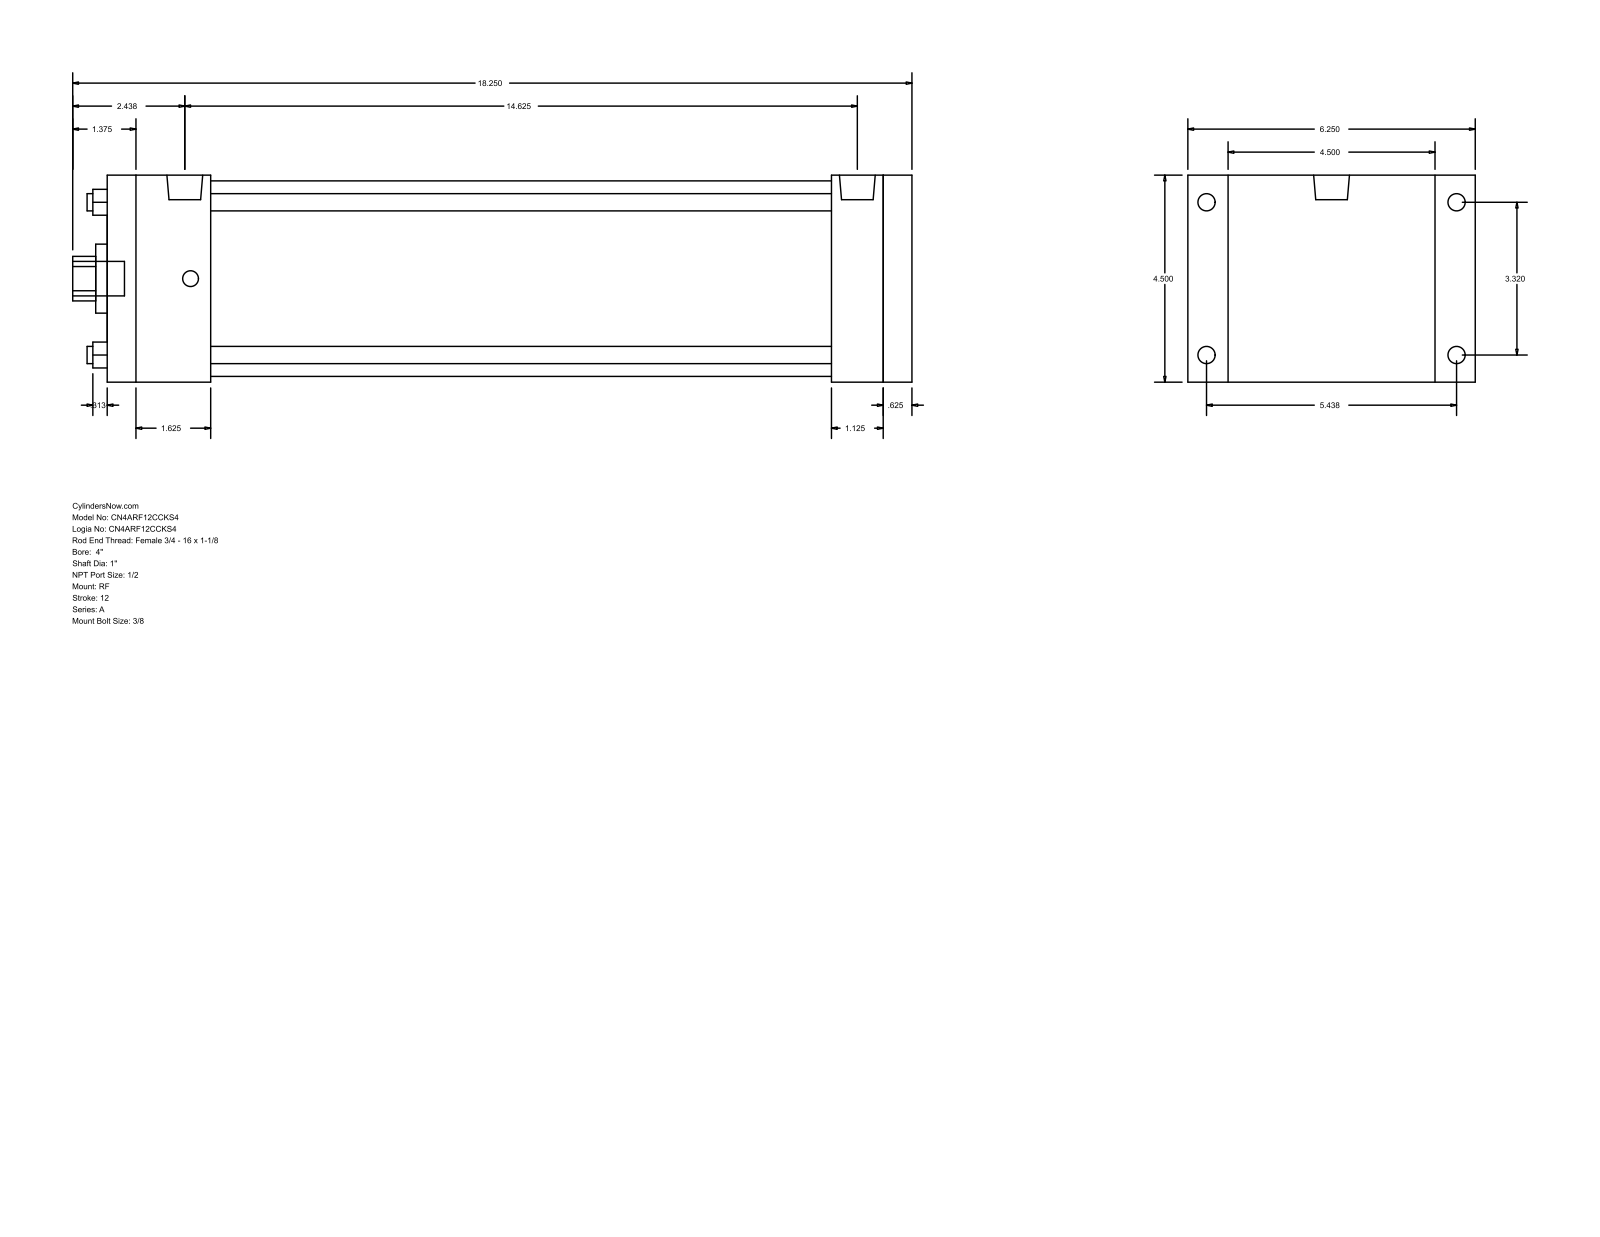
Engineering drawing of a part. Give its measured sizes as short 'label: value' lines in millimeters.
name: A_RF__0400_1
written by: GSSL Pune (CONFIG_CONTROL_DESIGN)
unit: mm
bodies: 0 solids, 92 faces (64 planar, 28 cylindrical, 0 other)
size: 463.55 × 158.75 × 114.3
holes: 4× ⌀9.53, 1× ⌀25.4, 1× ⌀38.1, 1× ⌀107.95
bosses: 4× ⌀9.53, 4× ⌀8.73, 2× ⌀19.77, 1× ⌀19.05
rounds: 1× R12.29
face distances: 114.3, 444.5, 15.87, 428.63, 22.23, 136.53, 400.05, 28.58, 44.45, 57.15
hole spacings: 59.62, 84.32, 119.25
